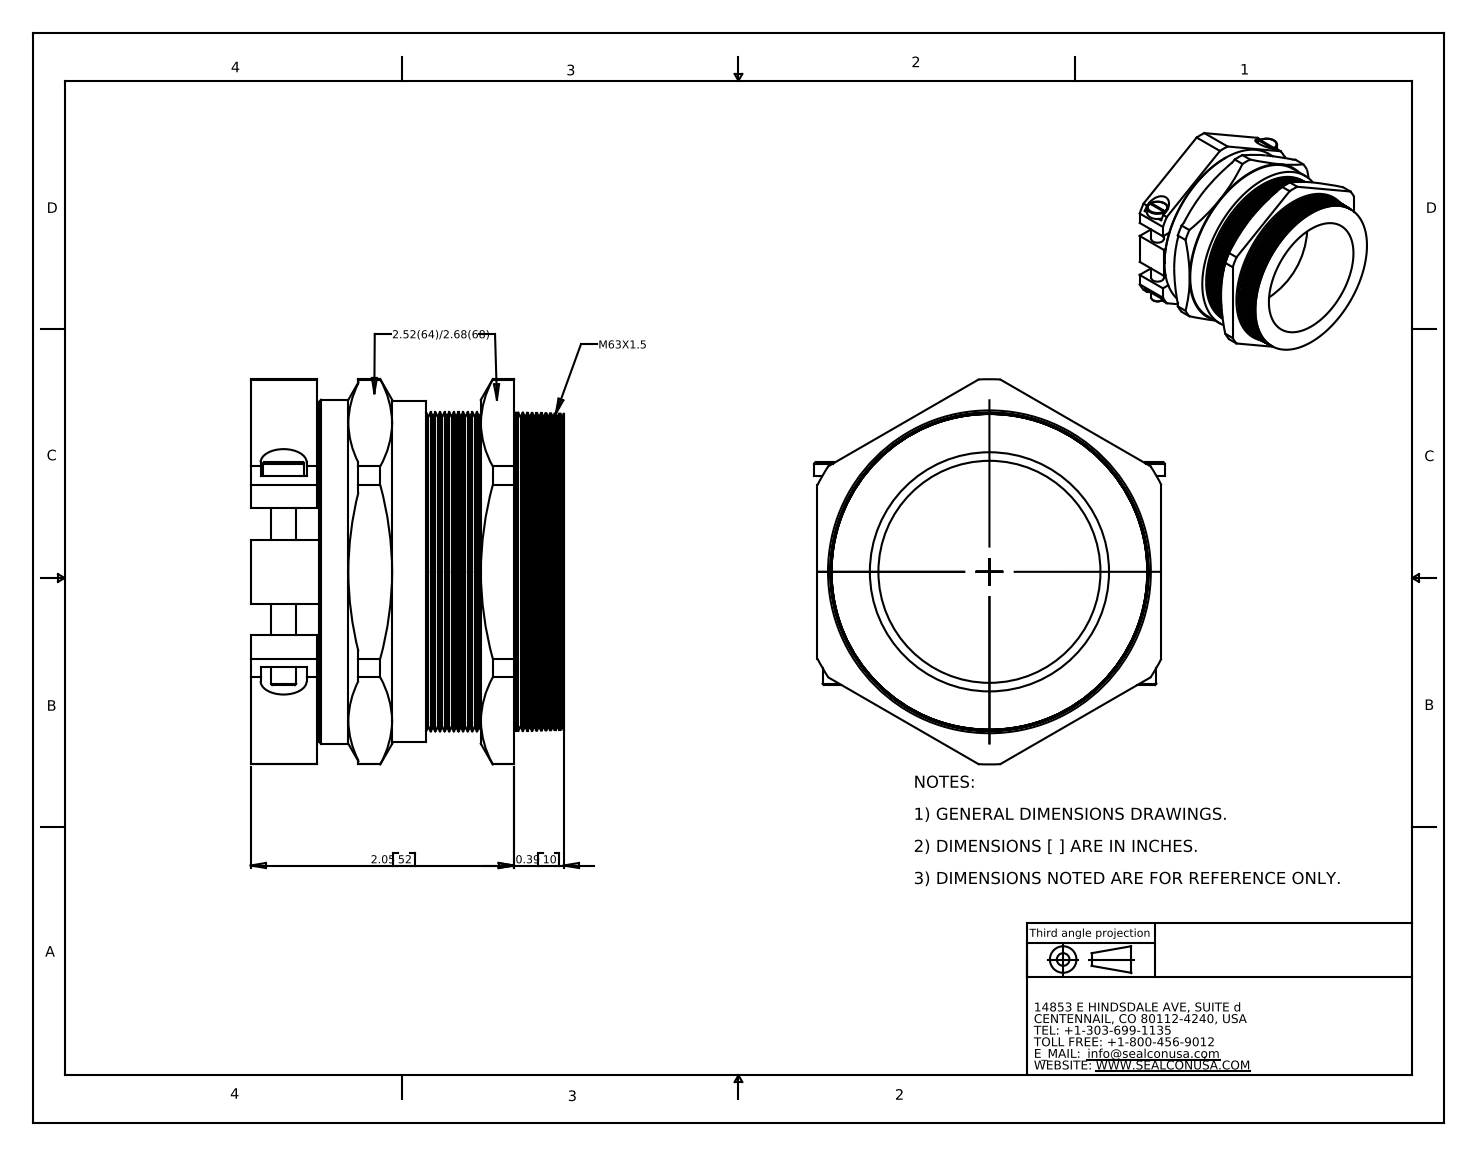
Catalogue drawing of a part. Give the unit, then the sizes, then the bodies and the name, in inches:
Units: inches
Overall size (bounding box): 3.002 × 2.73 × 2.439
Round holes (diameter × count): ⌀1.73 ×1, ⌀2.249 ×1
Round bosses / shafts (diameter × count): ⌀0.323 ×2, ⌀0.194 ×2, ⌀2.68 ×1, ⌀2.655 ×1, ⌀2.484 ×1
Partial cylindrical surfaces — rounded edges, fillets, slot ends (radius × count): R0.179 ×2, R1.501 ×1
Main face-to-face distances: 2.68, 0.76, 0.513, 0.248, 2.439, 1.926, 1.679, 0.02, 0.533, 0.228
Volume: 7.246 in³ · Surface area: 63.95 in²
Bodies: 3 solids, 313 faces (82 planar, 82 cylindrical, 149 other)
Part name (STEP PRODUCT): CD63MA-MZ
STEP written by: SolidWorks 2007 (CONFIG_CONTROL_DESIGN)
